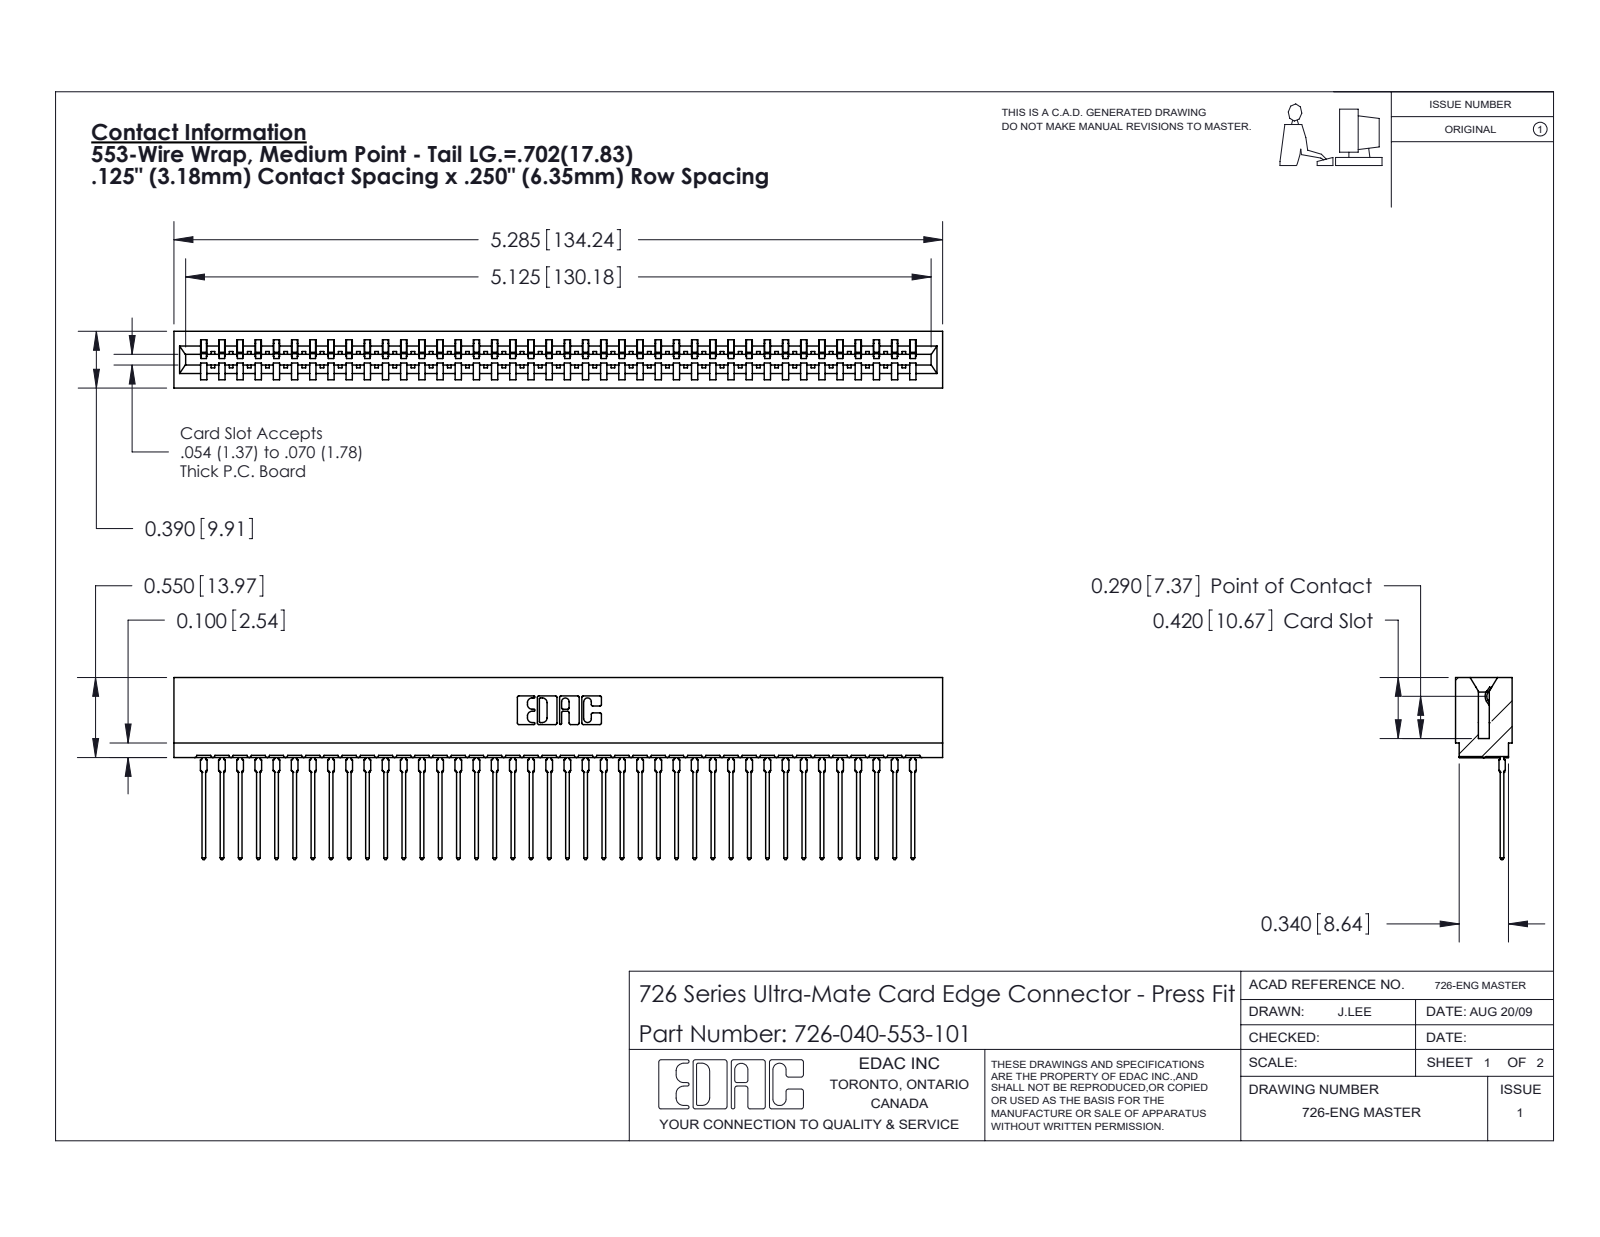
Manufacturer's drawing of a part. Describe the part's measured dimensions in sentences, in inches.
The part is named "726 Part_.515 Slot Depth - 01; 746-292-001_553; 726-040-553-101". Its 3-D file was written by "SolidWorks 2020 (CONFIG_CONTROL_DESIGN)". It is 41 solids with 4417 faces: 2575 planar, 802 cylindrical and 1040 other. Overall it measures 5.285 by 1.251 by 0.39 inches. Its volume is 0.742 cubic inches and its surface area 29.84 square inches. Partial cylindrical surfaces (rounded edges, fillets, slot ends): 80 of radius 0.021, 41 of radius 0.015, 22 of radius 0.01, 6 of radius 0.007, 6 of radius 0.031, 4 of radius 0.005, 4 of radius 0.011, 3 of radius 0.026. The main face-to-face distances are 0.057, 0.333, 0.39, 0.25, 0.025, 0.307, 0.083, 0.275, 0.365, 0.032.
